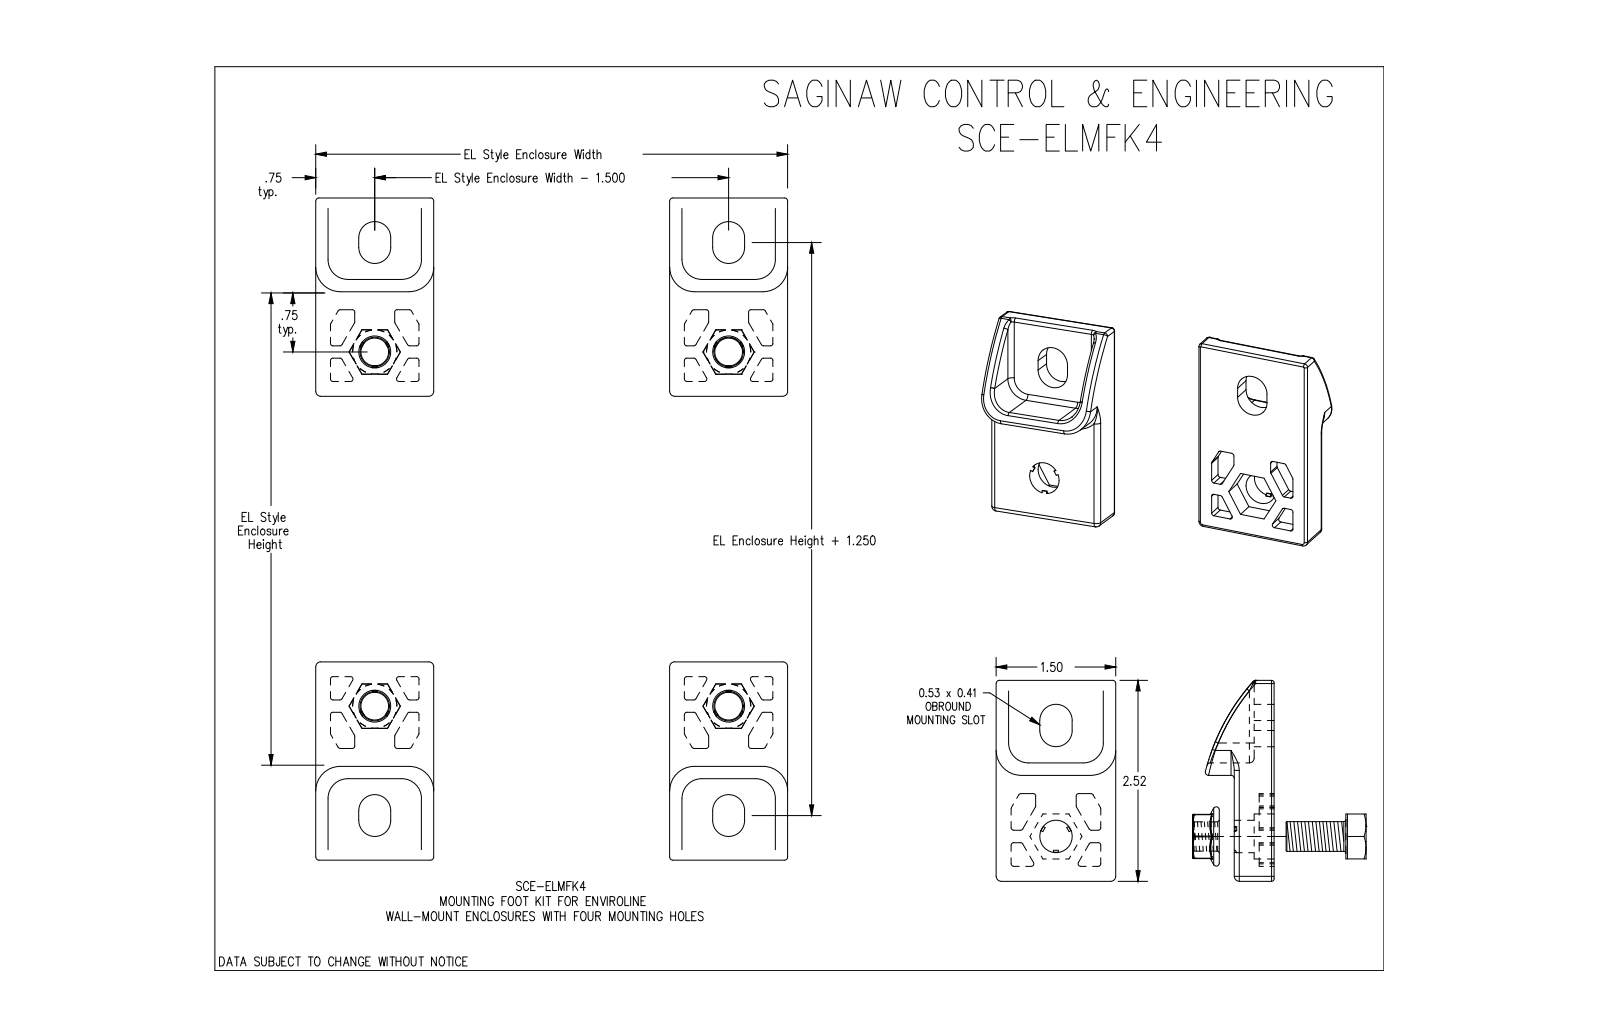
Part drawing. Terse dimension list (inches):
name: SCE-ELMFK4
written by: SolidWorks 2019 (AUTOMOTIVE_DESIGN)
unit: in
bodies: 12 solids, 804 faces (328 planar, 224 cylindrical, 252 other)
size: 8.415 × 6 × 1.004
volume: 6.784 in³; area: 70.67 in²
holes: 4× ⌀0.367, 4× ⌀0.406
bosses: 4× ⌀0.563, 4× ⌀0.373
rounds: 88× R0.031, 24× R0.01, 18× R0.041, 8× R0.063, 8× R0.203, 8× R0.25, 6× R0.06, 6× R0.062
face distances: 0.25, 0.5, 4.5, 1.5, 0.187, 6, 3, 0.156, 4.859, 0.063
hole spacings: 4.5, 6.364, 4.499, 6.363
